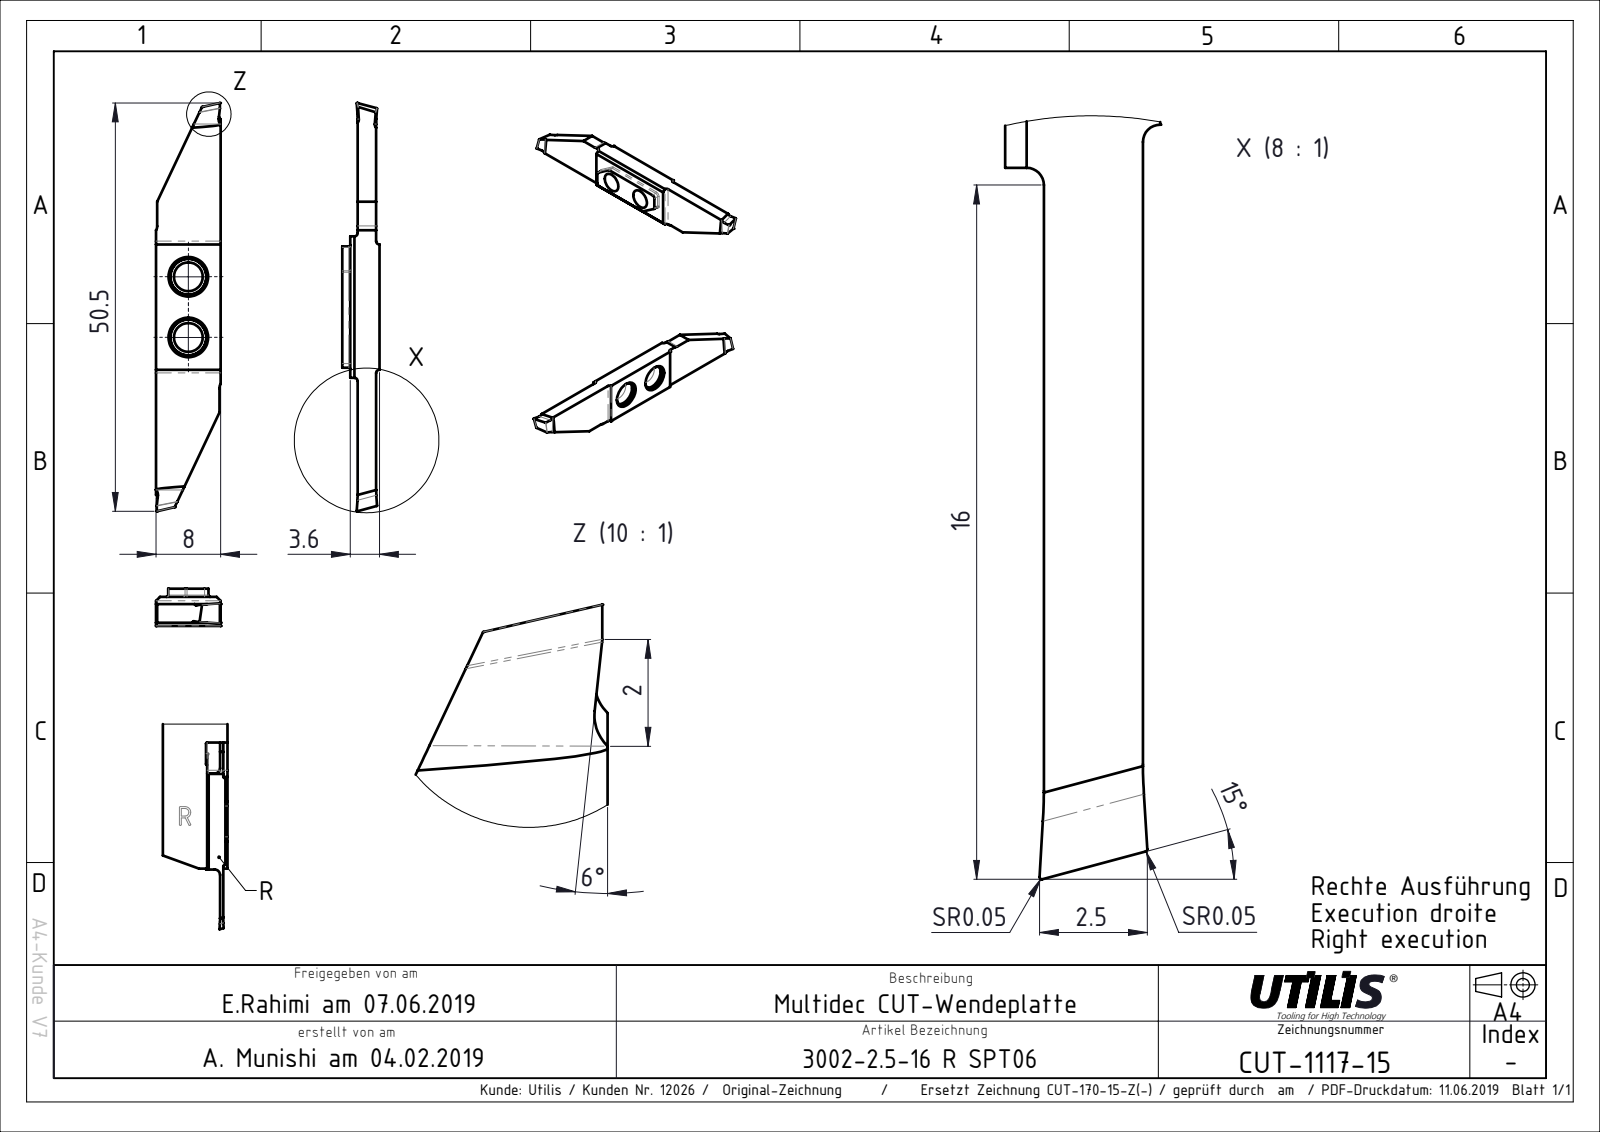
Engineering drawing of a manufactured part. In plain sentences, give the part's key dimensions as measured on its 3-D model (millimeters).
The part is named "CUT-1117; ASME Y14.5". Its 3-D file was written by "FormatWorks Professional (AP242_MANAGED_MODEL_BASED_3D_ENGINEERING_MIM_LF)". It is 1 solid with 40 faces: 24 planar, 16 cylindrical and 0 other. Overall it measures 50.5 by 8 by 3.6 millimeters. Its volume is 855 cubic millimeters and its surface area 991 square millimeters. Round holes: 2 of diameter 3.55. Partial cylindrical surfaces (rounded edges, fillets, slot ends): 4 of radius 0.4, 2 of radius 1. The main face-to-face distances are 2.3, 2.7, 0.4, 0.9, 3.2, 3.6, 8, 18.09, 7.85, 7.7. The hole center spacings are 7.5.
